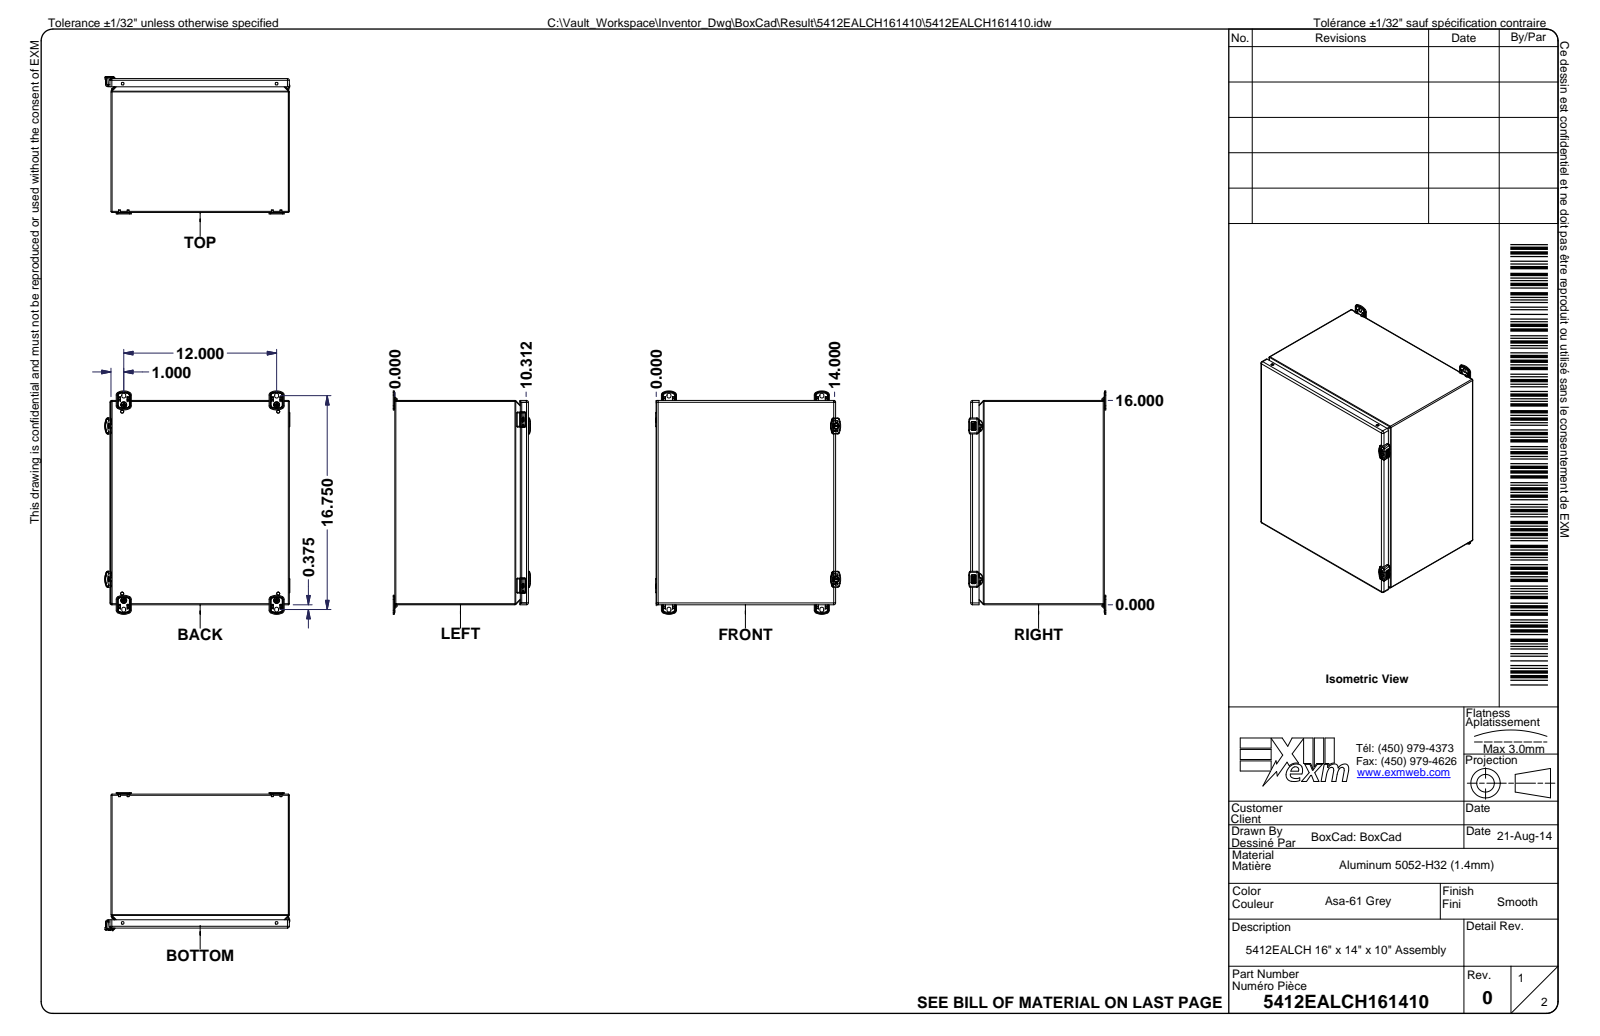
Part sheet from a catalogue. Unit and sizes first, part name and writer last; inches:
Units: inches
Overall size (bounding box): 17.496 × 14.503 × 10.76
Round holes (diameter × count): ⌀0.165 ×4, ⌀0.173 ×4, ⌀0.197 ×4, ⌀0.197 ×4, ⌀0.236 ×4, ⌀0.236 ×4, ⌀0.32 ×4, ⌀0.03 ×2, ⌀0.175 ×2, ⌀0.201 ×2, ⌀0.24 ×2, ⌀0.339 ×2
Round bosses / shafts (diameter × count): ⌀0.232 ×8, ⌀0.236 ×6, ⌀0.5 ×4, ⌀0.3 ×4, ⌀0.193 ×4, ⌀0.197 ×3, ⌀0.412 ×2, ⌀0.394 ×2
Partial cylindrical surfaces — rounded edges, fillets, slot ends (radius × count): R0.02 ×257, R0.01 ×209, R0.039 ×92, R0.004 ×64, R0.008 ×60, R0.059 ×57, R0.031 ×35, R0.005 ×33
Main face-to-face distances: 0.053, 13.947, 15.947, 0.053, 10.433, 10.38, 10.486, 10.433, 0.236, 0.304
Hole centre spacings: 12, 19.118, 0.546, 12.25, 14.781, 12.137, 13, 18.652
Volume: 77.04 in³ · Surface area: 2 761 in²
Bodies: 59 solids, 8409 faces (3583 planar, 2002 cylindrical, 2824 other)
Part name (STEP PRODUCT): 5412EALCH161410; 5412EALCH161410B; 5412EALCH161410B-P; STK-A-70469-1 (+8 more)
STEP written by: Autodesk Inventor 2020 (AUTOMOTIVE_DESIGN)
